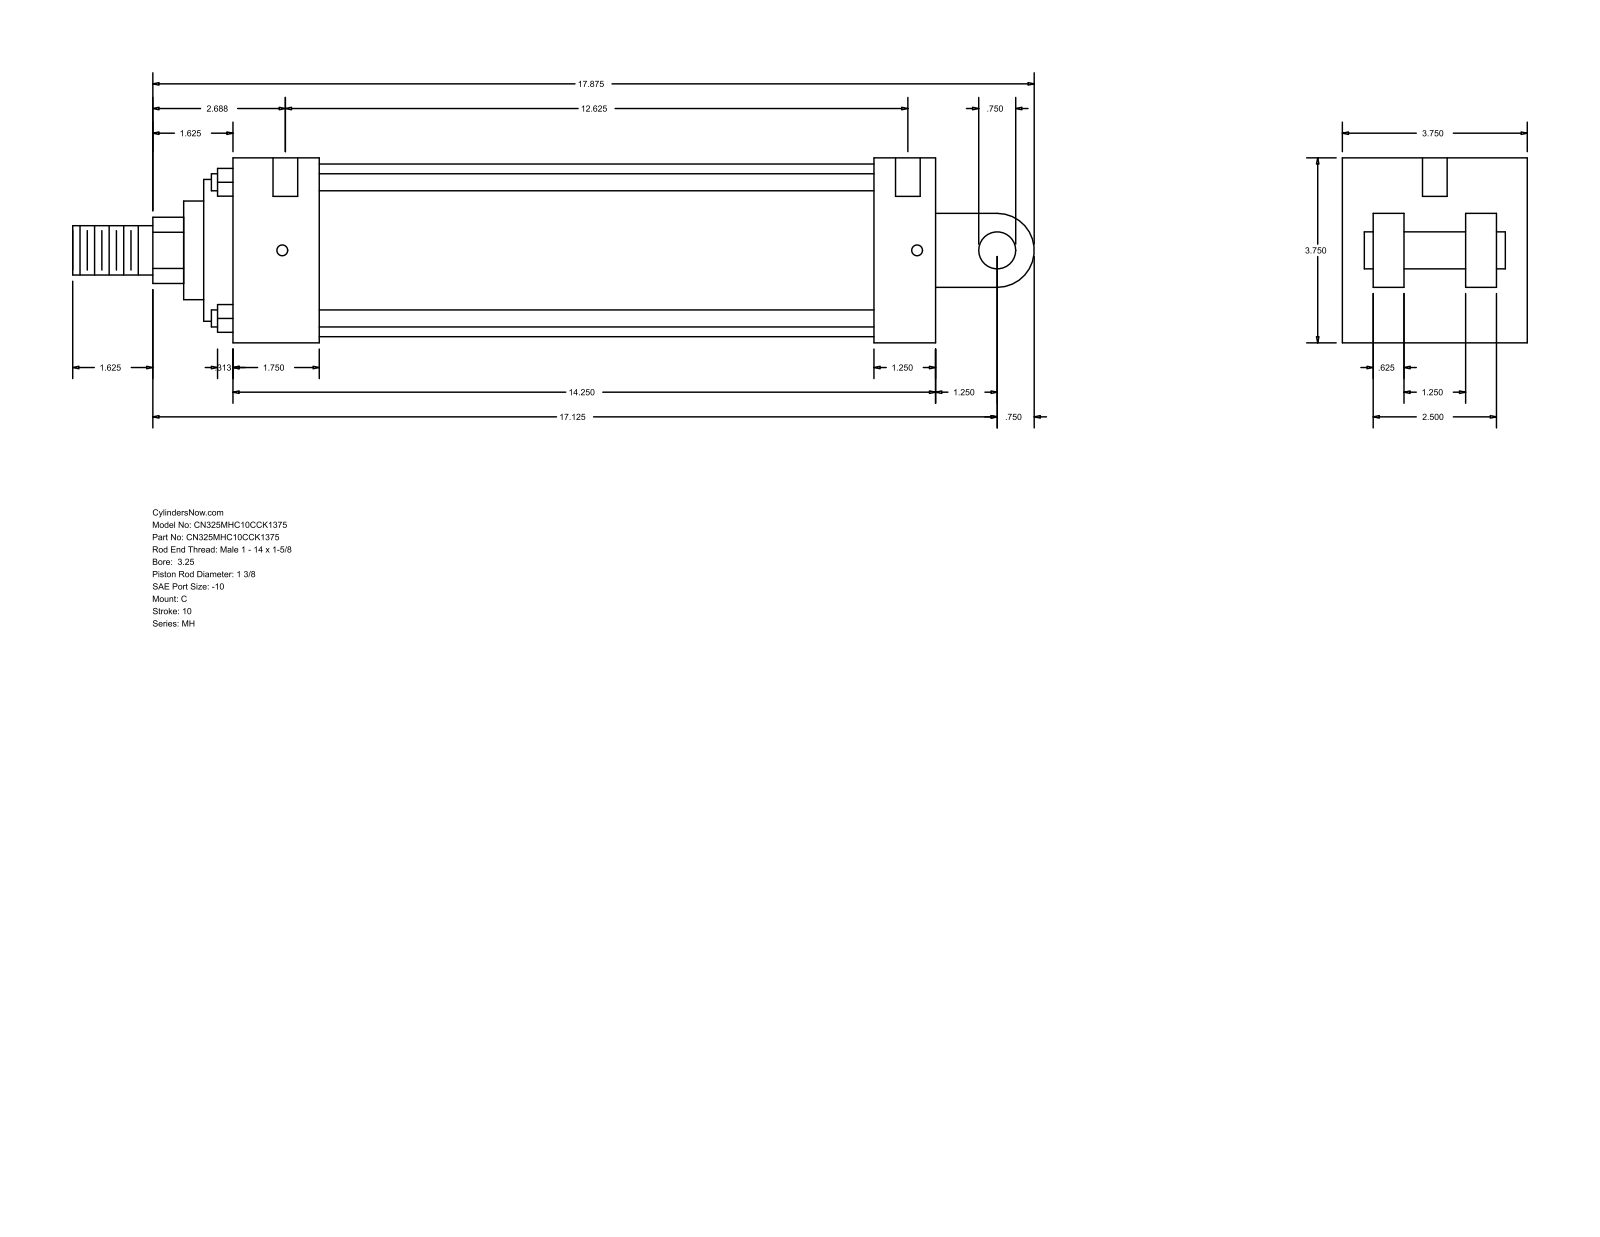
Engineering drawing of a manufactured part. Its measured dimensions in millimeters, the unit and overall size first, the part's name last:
Units: millimetres
Overall size (bounding box): 495.3 × 95.25 × 95.25
Round holes (diameter × count): ⌀5.56 ×4, ⌀12.7 ×2
Round bosses / shafts (diameter × count): ⌀8.76 ×4, ⌀88.9 ×1, ⌀73.03 ×1, ⌀50.8 ×1, ⌀34.92 ×1, ⌀25.4 ×1, ⌀19.05 ×1
Partial cylindrical surfaces — rounded edges, fillets, slot ends (radius × count): R17.06 ×1, R19.05 ×1
Main face-to-face distances: 95.24, 15.87, 63.5, 361.96, 79.37, 31.74, 47.63, 44.45, 330.21, 285.76
Hole centre spacings: 327.03, 1.59, 4.76, 320.68, 322.27, 325.44
Bodies: 0 solids, 101 faces (71 planar, 30 cylindrical, 0 other)
Part name (STEP PRODUCT): MH_C__0325_1.375
STEP written by: GSSL Pune (CONFIG_CONTROL_DESIGN)
